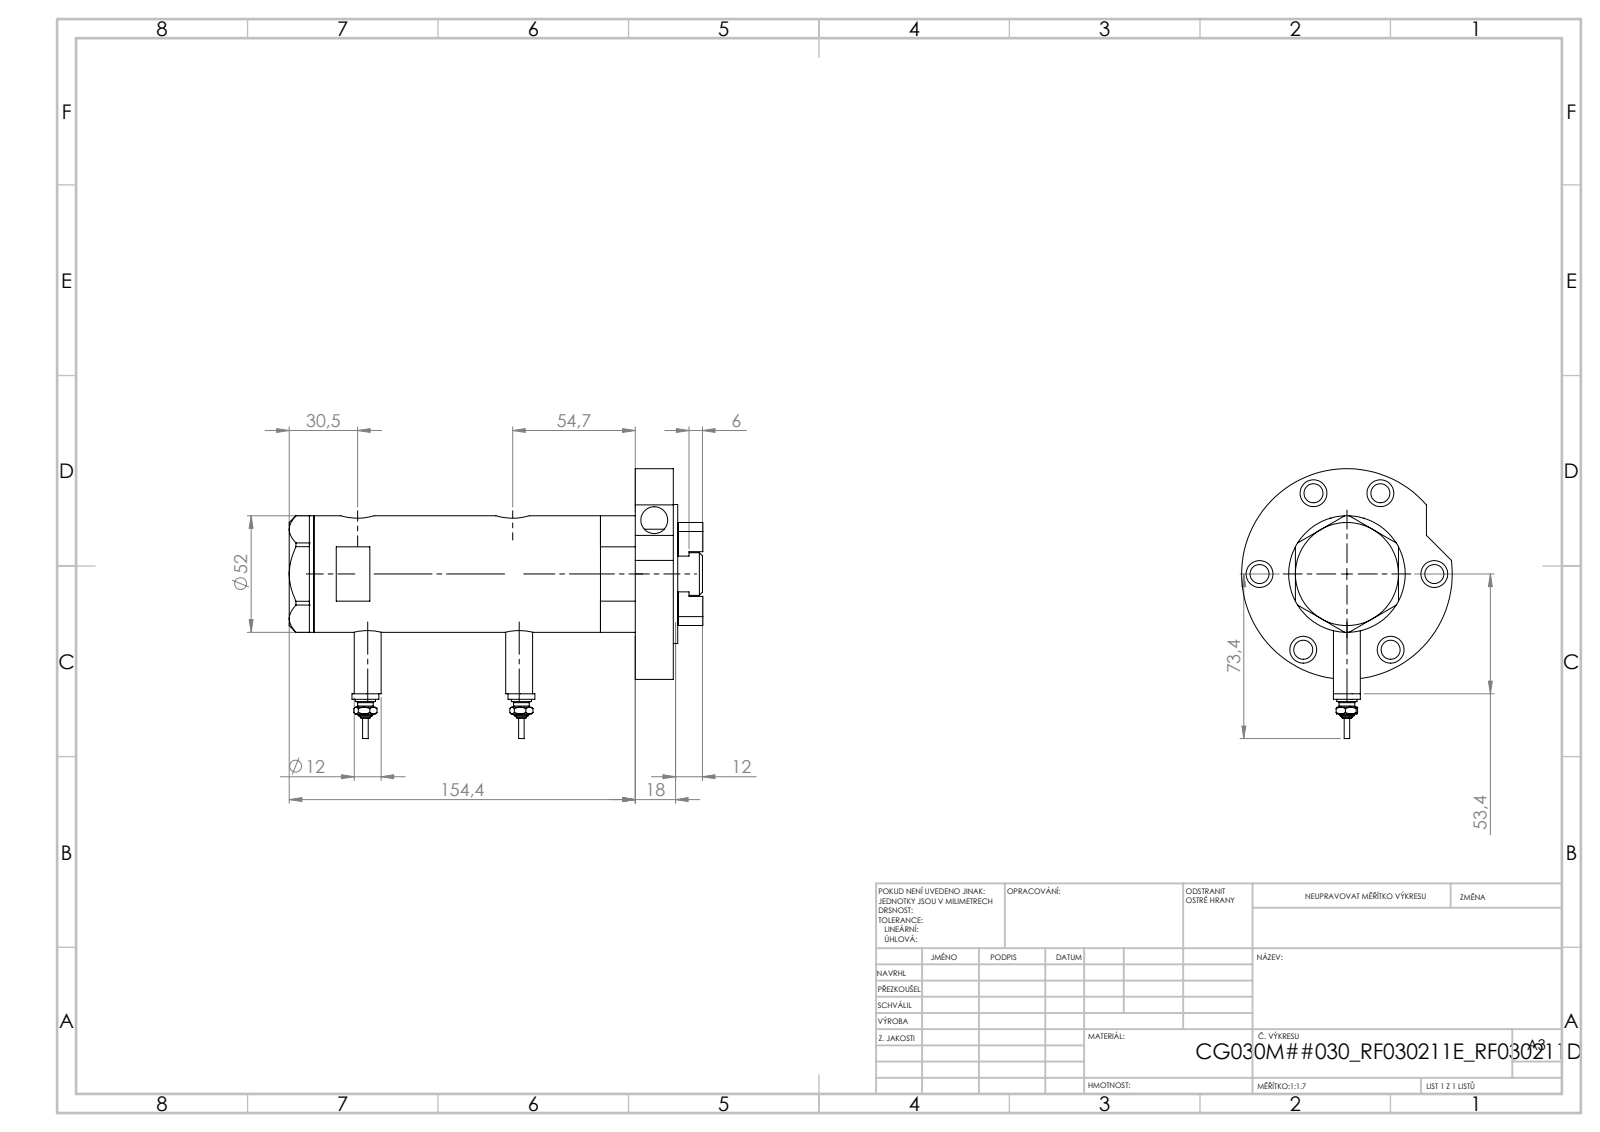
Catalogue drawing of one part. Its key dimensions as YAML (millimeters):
part_name: "V270CG_SWITCH; V270CG_VC; V270CG_MIDDLE; V270CG_BACK (+3 more)"
step_written_by: "SolidWorks 2019 (CONFIG_CONTROL_DESIGN)"
units: millimeters
bodies: {solids: 9, faces: 330, planar: 130, cylindrical: 126, other: 74}
overall_size: [179.22, 105.3, 94]
volume: 408394
surface_area: 103850
round_holes:
  - {diameter: 12, count: 7}
  - {diameter: 8.5, count: 6}
  - {diameter: 5.1, count: 4}
  - {diameter: 9, count: 4}
  - {diameter: 5, count: 2}
  - {diameter: 9.73, count: 2}
  - {diameter: 12.5, count: 2}
  - {diameter: 15, count: 2}
  - {diameter: 6.5, count: 1}
  - {diameter: 20, count: 1}
  - {diameter: 21.5, count: 1}
  - {diameter: 30, count: 1}
round_bosses_or_shafts:
  - {diameter: 12, count: 3}
  - {diameter: 9, count: 2}
  - {diameter: 7, count: 2}
  - {diameter: 4.34, count: 2}
  - {diameter: 2.4, count: 2}
  - {diameter: 94, count: 1}
  - {diameter: 62, count: 1}
  - {diameter: 52, count: 1}
face_to_face_distances: [17, 135.45, 152.45, 2, 154.45, 10.99, 19, 23.81, 111.64, 128.64]
hole_center_spacings: [39, 16.74, 37.57, 46.81, 2.9, 4.5, 10, 22.37]
